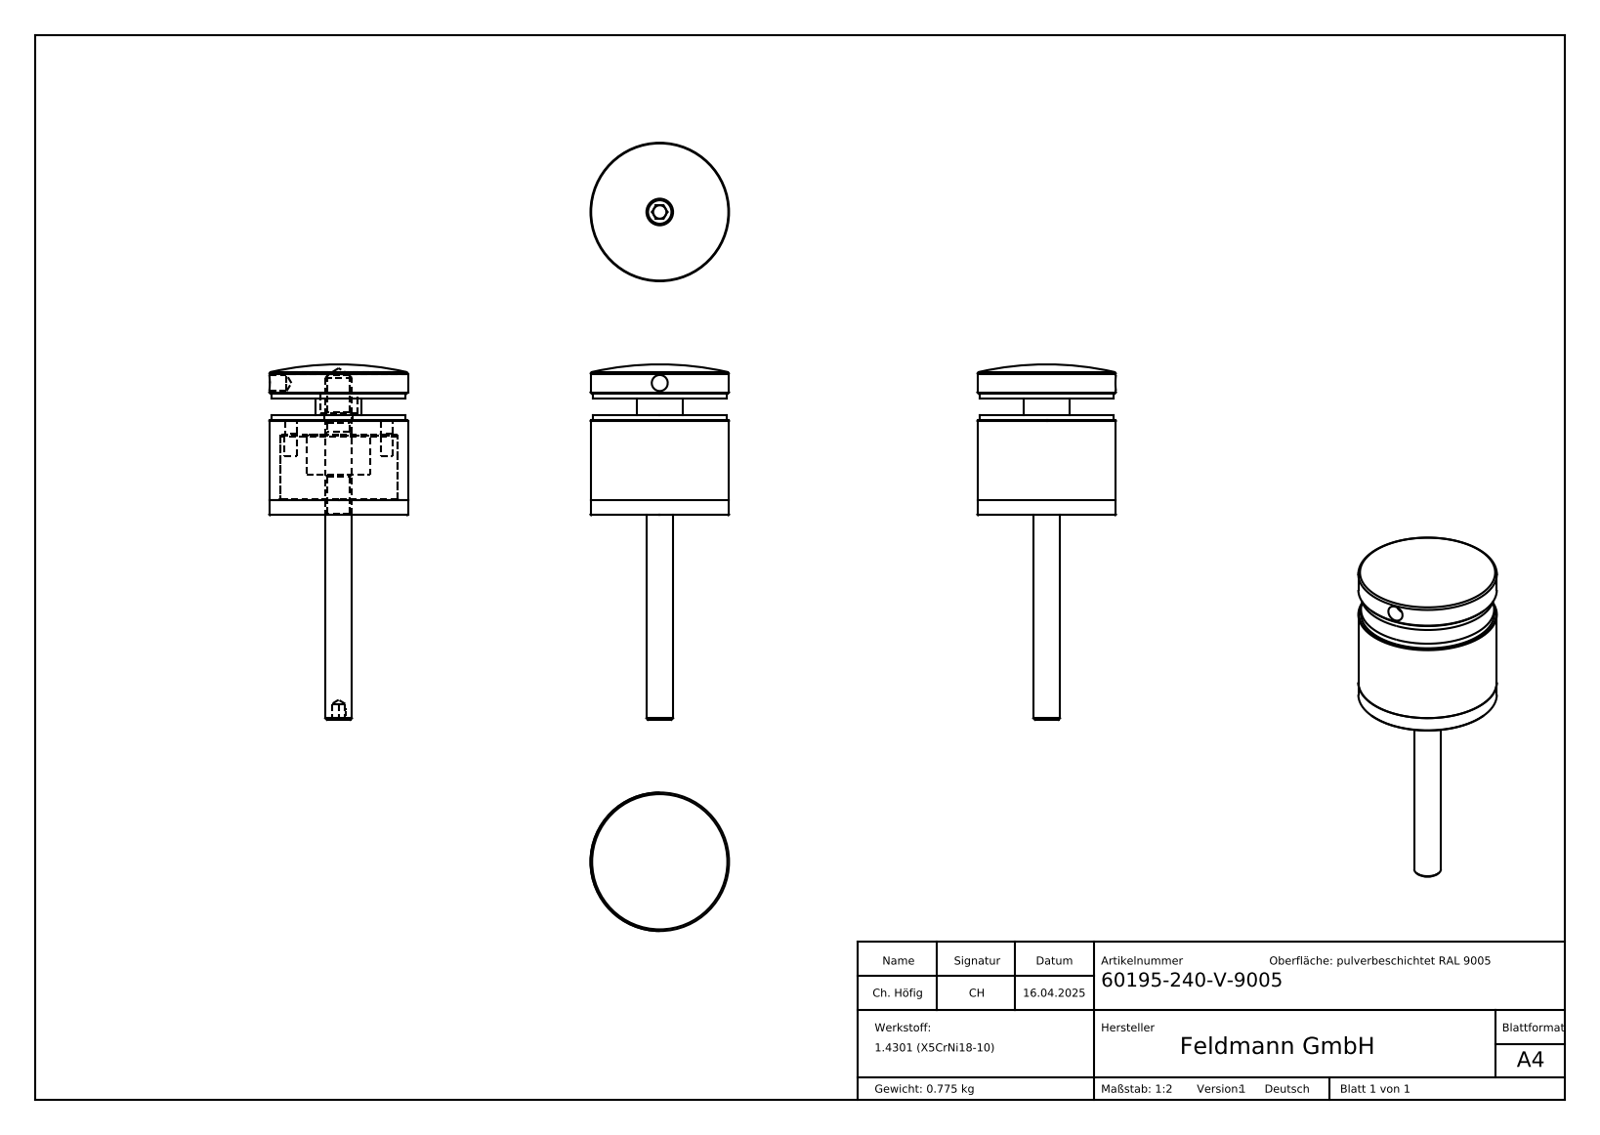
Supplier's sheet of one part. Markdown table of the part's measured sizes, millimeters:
| quantity | value |
| --- | --- |
| part name | 60195-240-V-9005 Teil5_60195-240-V-9005 Teil5; 60195-240-V-9005 Teil4_60195-240-V-9005 Teil4; 60195-240-V-9005 Teil1_60195-240-V-9005 Teil1; 60195-240-V-9005 Teil3_60195-240-V-9005 Teil3 (+3 more) |
| STEP written by | SolidWorks 2018 (CONFIG_CONTROL_DESIGN) |
| units | millimeters |
| bodies | 6 solids, 644 faces (333 planar, 21 cylindrical, 290 other) |
| overall size | 133.44 × 52 × 52 |
| volume | 104 781 mm³ |
| surface area | 42 071 mm² |
| round holes (diameter × count) | 4.4 × 2, 4.5 × 2, 6 × 1, 8.5 × 1, 10.5 × 1, 14 × 1, 24 × 1, 44.1 × 1 |
| round bosses / shafts (diameter × count) | 52 × 1, 50 × 1, 44 × 1, 17 × 1, 10 × 1 |
| main face-to-face distances | 8, 2, 10, 5.6, 30, 35.6, 45.6, 37.6, 6, 43.6 |
| hole center spacings | 18, 36 |
